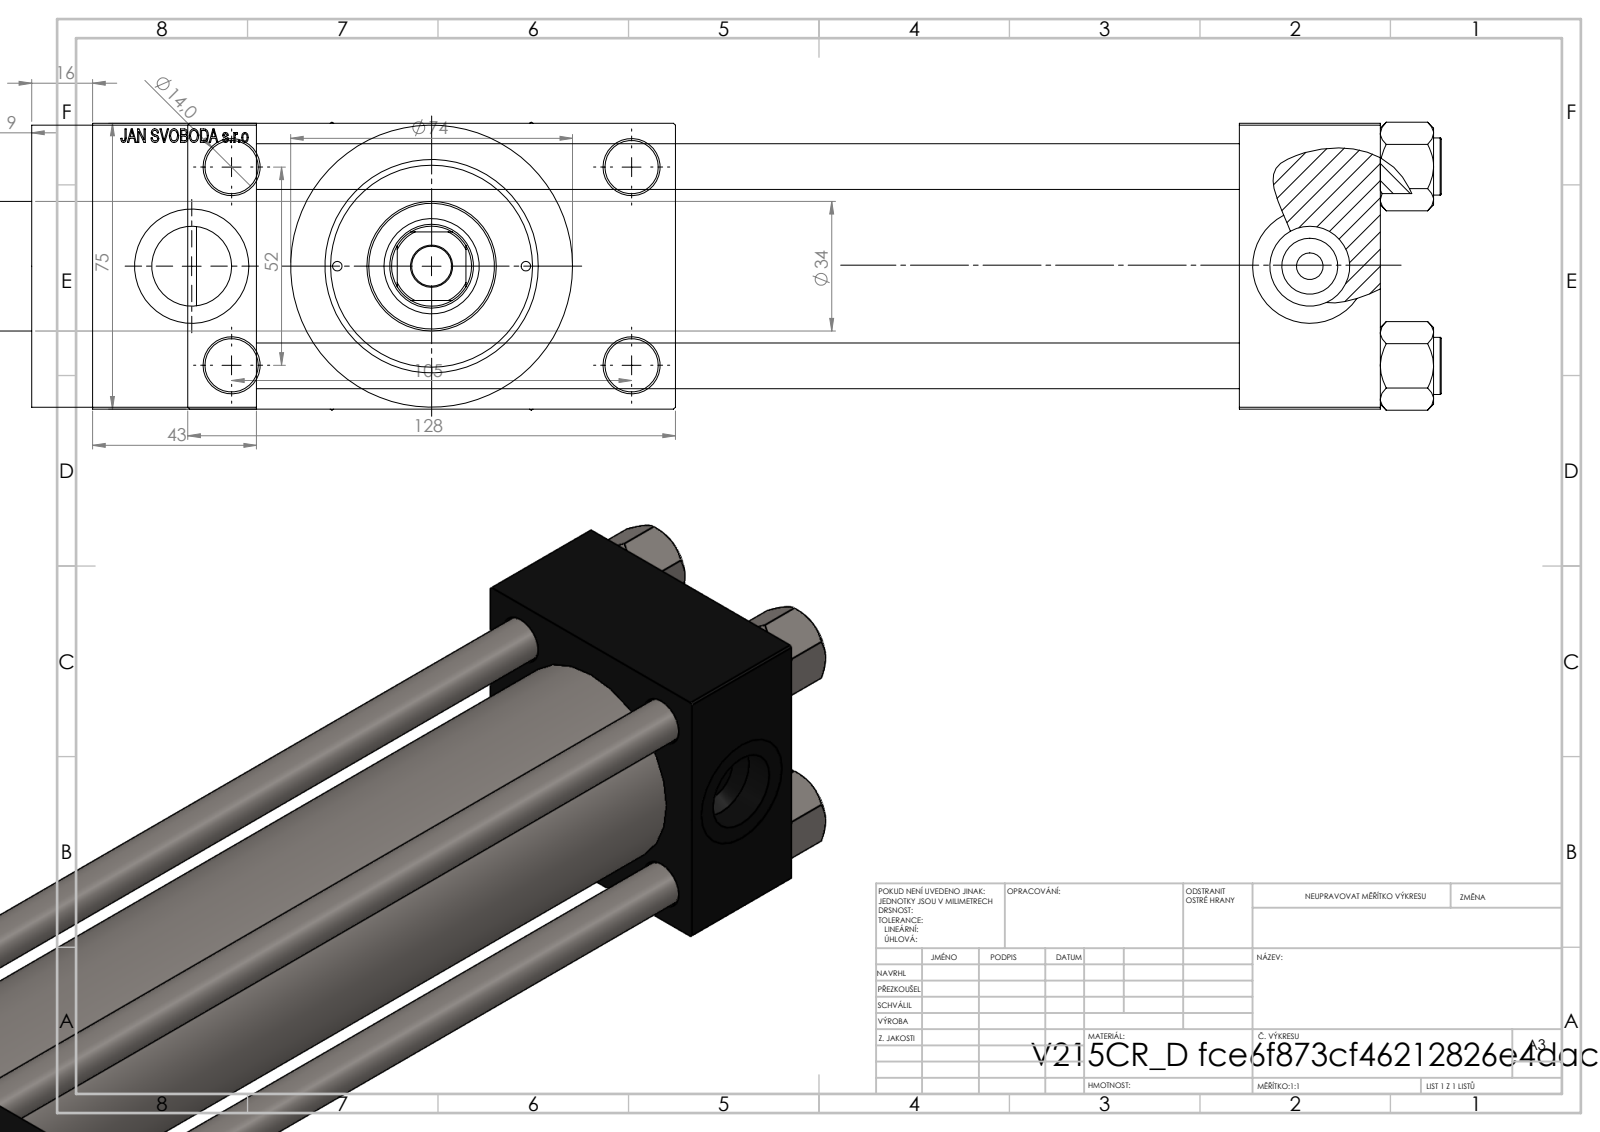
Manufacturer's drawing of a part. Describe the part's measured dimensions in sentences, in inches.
The part is named "NUT_M5_D; V215CR_D_Body; V215_VC_A; V215CR_VCP_D (+1 more)". Its 3-D file was written by "SolidWorks 2019 (CONFIG_CONTROL_DESIGN)". It is 11 solids with 1111 faces: 499 planar, 92 cylindrical and 520 other. Overall it measures 15.551 by 5.039 by 2.974 inches. Its volume is 64.93 cubic inches and its surface area 429.5 square inches. Round holes: 4 of diameter 0.472, 4 of diameter 0.551, 2 of diameter 0.098, 2 of diameter 0.276, 2 of diameter 0.825, 2 of diameter 1.181, 1 of diameter 0.413, 1 of diameter 0.866, 1 of diameter 0.984, 1 of diameter 1.614, 1 of diameter 1.969, 1 of diameter 2.087. Round bosses or shafts: 4 of diameter 0.591, 1 of diameter 2.913, 1 of diameter 2.205, 1 of diameter 1.339. Partial cylindrical surfaces (rounded edges, fillets, slot ends): 1 of radius 0.413. The main face-to-face distances are 2.953, 10.157, 1.457, 11.614, 1.043, 13.307, 11.85, 1.693, 3.996, 0.63. The hole center spacings are 1.031, 1.037, 1.456, 1.497, 2.059, 2.253, 2.3, 2.307.
